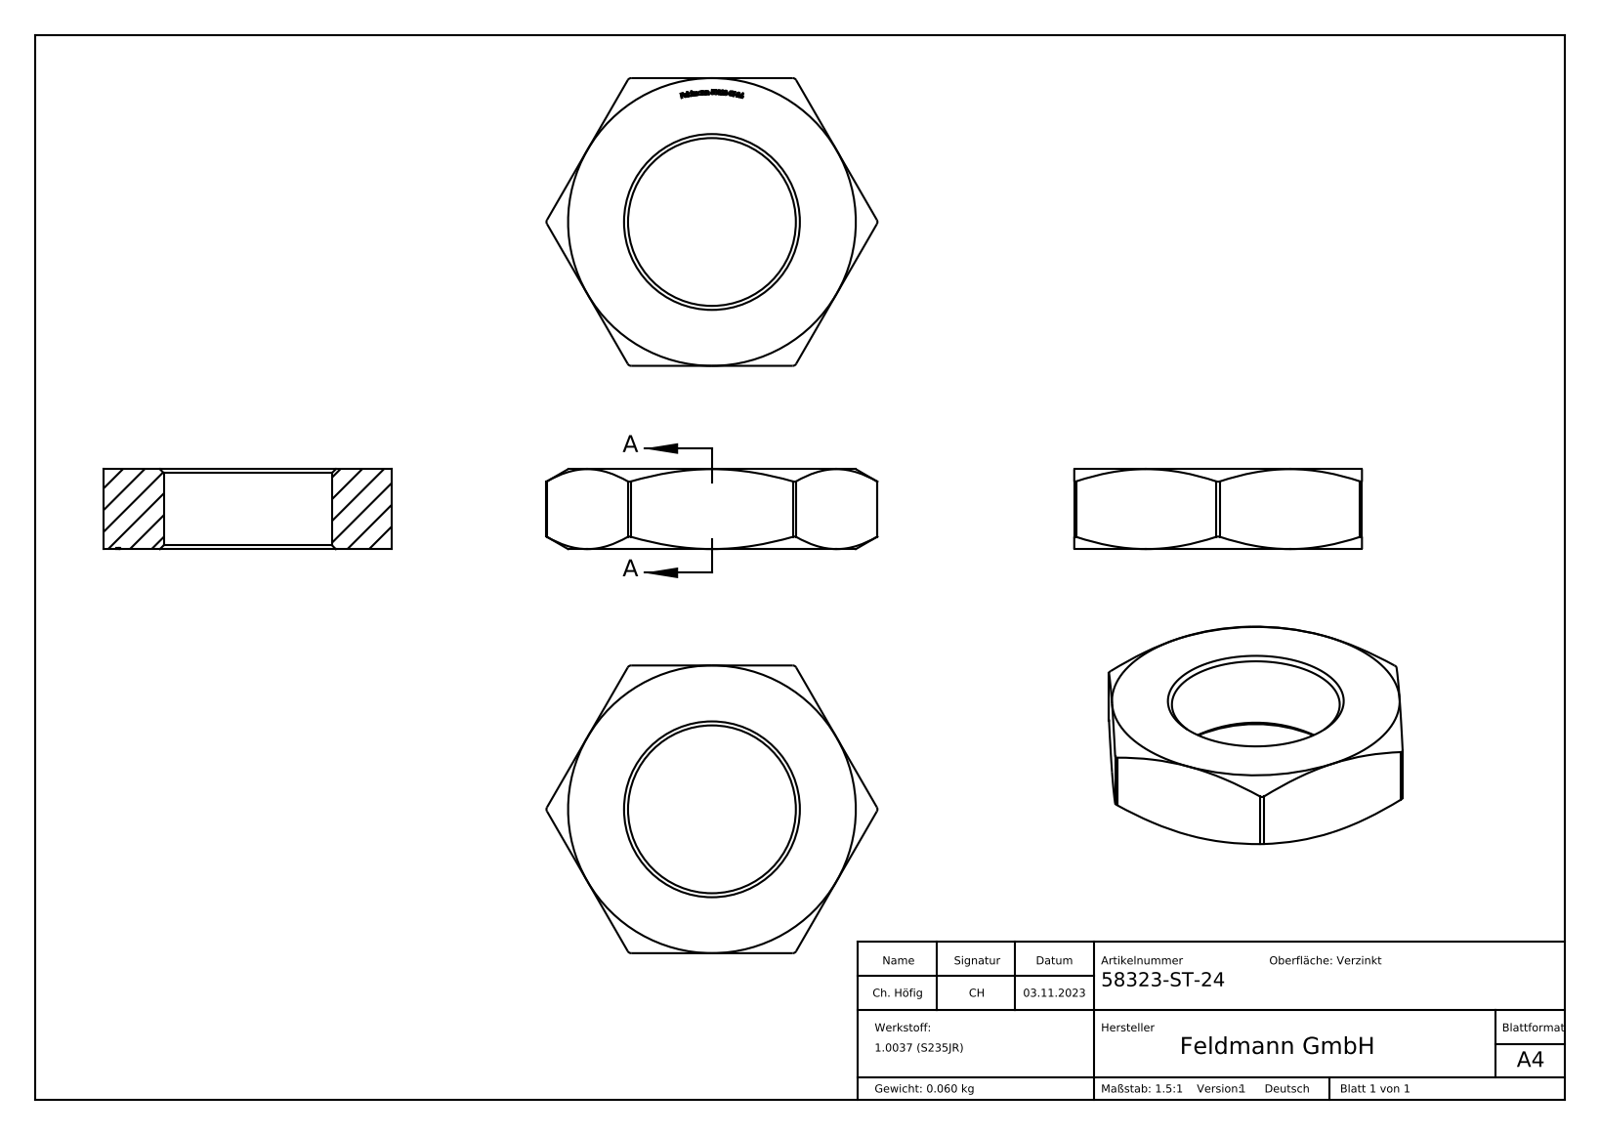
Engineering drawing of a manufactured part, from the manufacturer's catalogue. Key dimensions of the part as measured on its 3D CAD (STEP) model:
Part name (STEP PRODUCT): 58323-ST-24
STEP written by: SolidWorks 2018 (CONFIG_CONTROL_DESIGN)
Units: millimetres
Bodies: 1 solid, 291 faces (142 planar, 7 cylindrical, 142 other)
Overall size (bounding box): 41.41 × 36 × 10
Volume: 7 641 mm³ · Surface area: 3 317 mm²
Round holes (diameter × count): ⌀21 ×1
Partial cylindrical surfaces — rounded edges, fillets, slot ends (radius × count): R0.5 ×6
Main face-to-face distances: 10, 36, 9.9, 0.44, 0.39, 0.49, 0.73, 0.53, 0.31, 0.4
